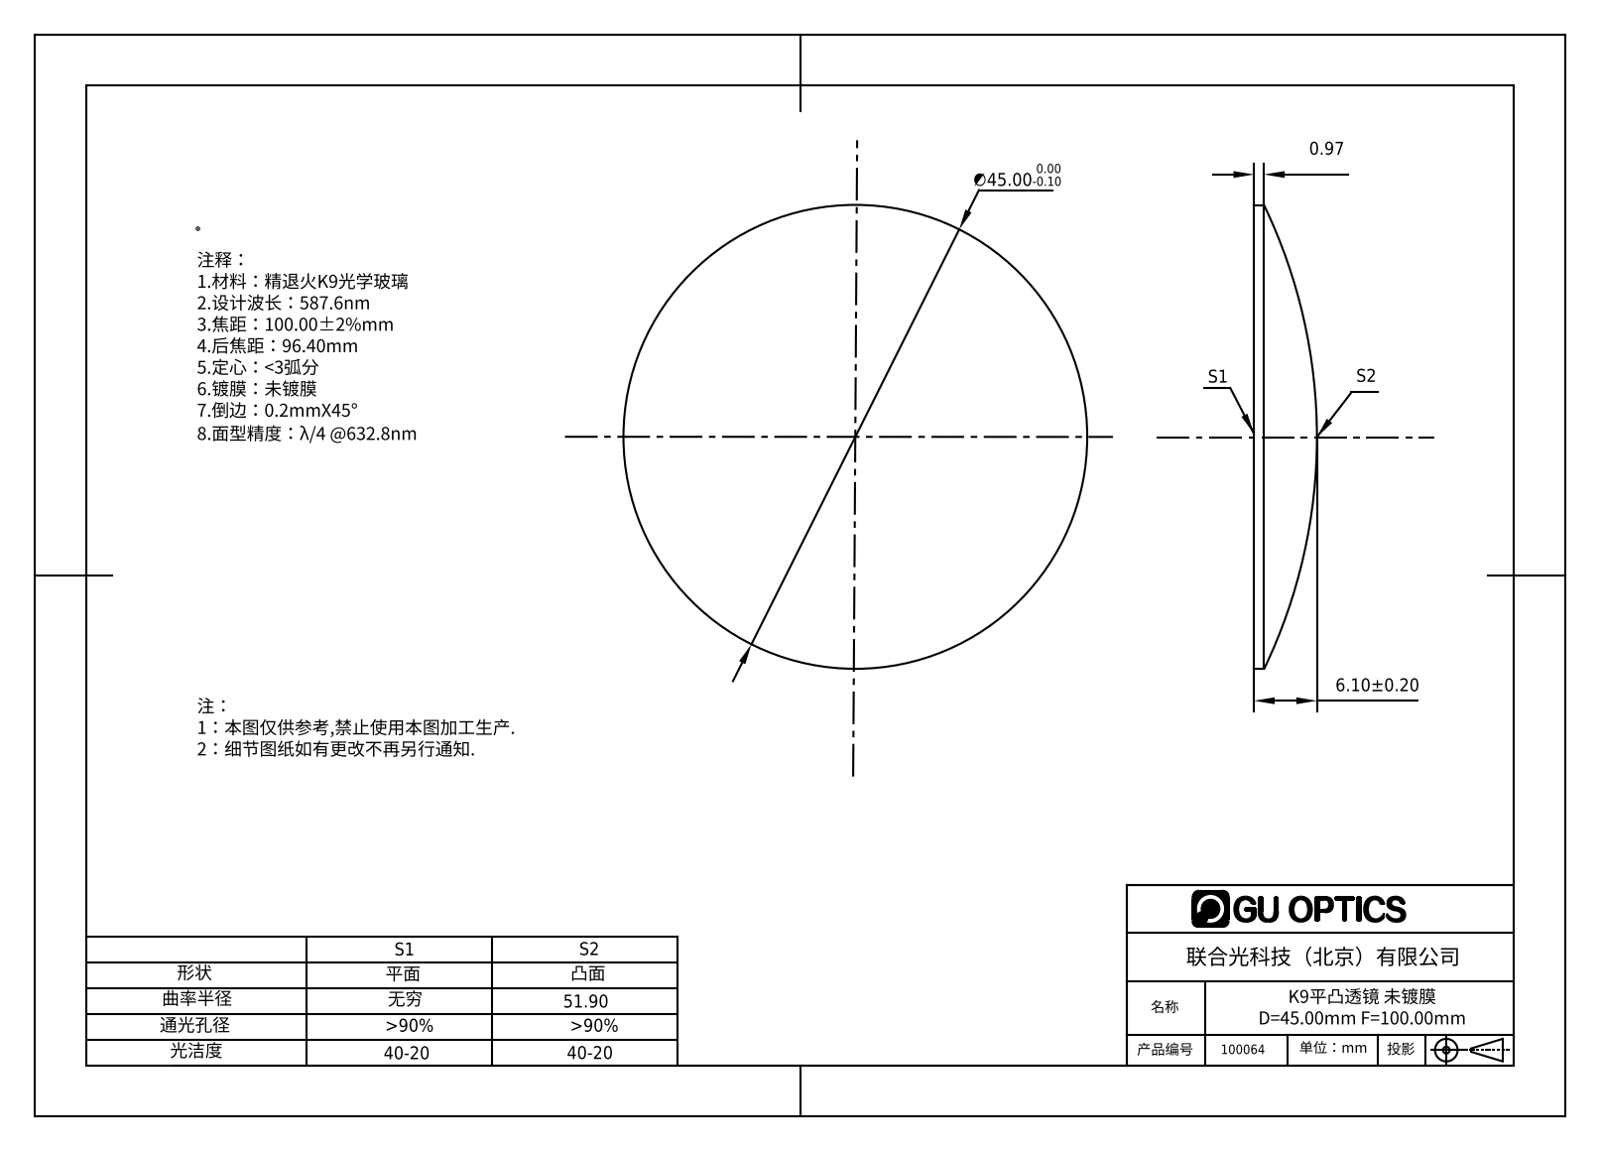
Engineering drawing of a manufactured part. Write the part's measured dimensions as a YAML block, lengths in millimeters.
part_name: "100064"
step_written_by: "SolidWorks 2016 (AUTOMOTIVE_DESIGN)"
units: millimeters
bodies: {solids: 1, faces: 5, planar: 1, cylindrical: 2, other: 2}
overall_size: [45, 45, 6.1]
volume: 5693
surface_area: 3401
round_bosses_or_shafts:
  - {diameter: 45, count: 1}
